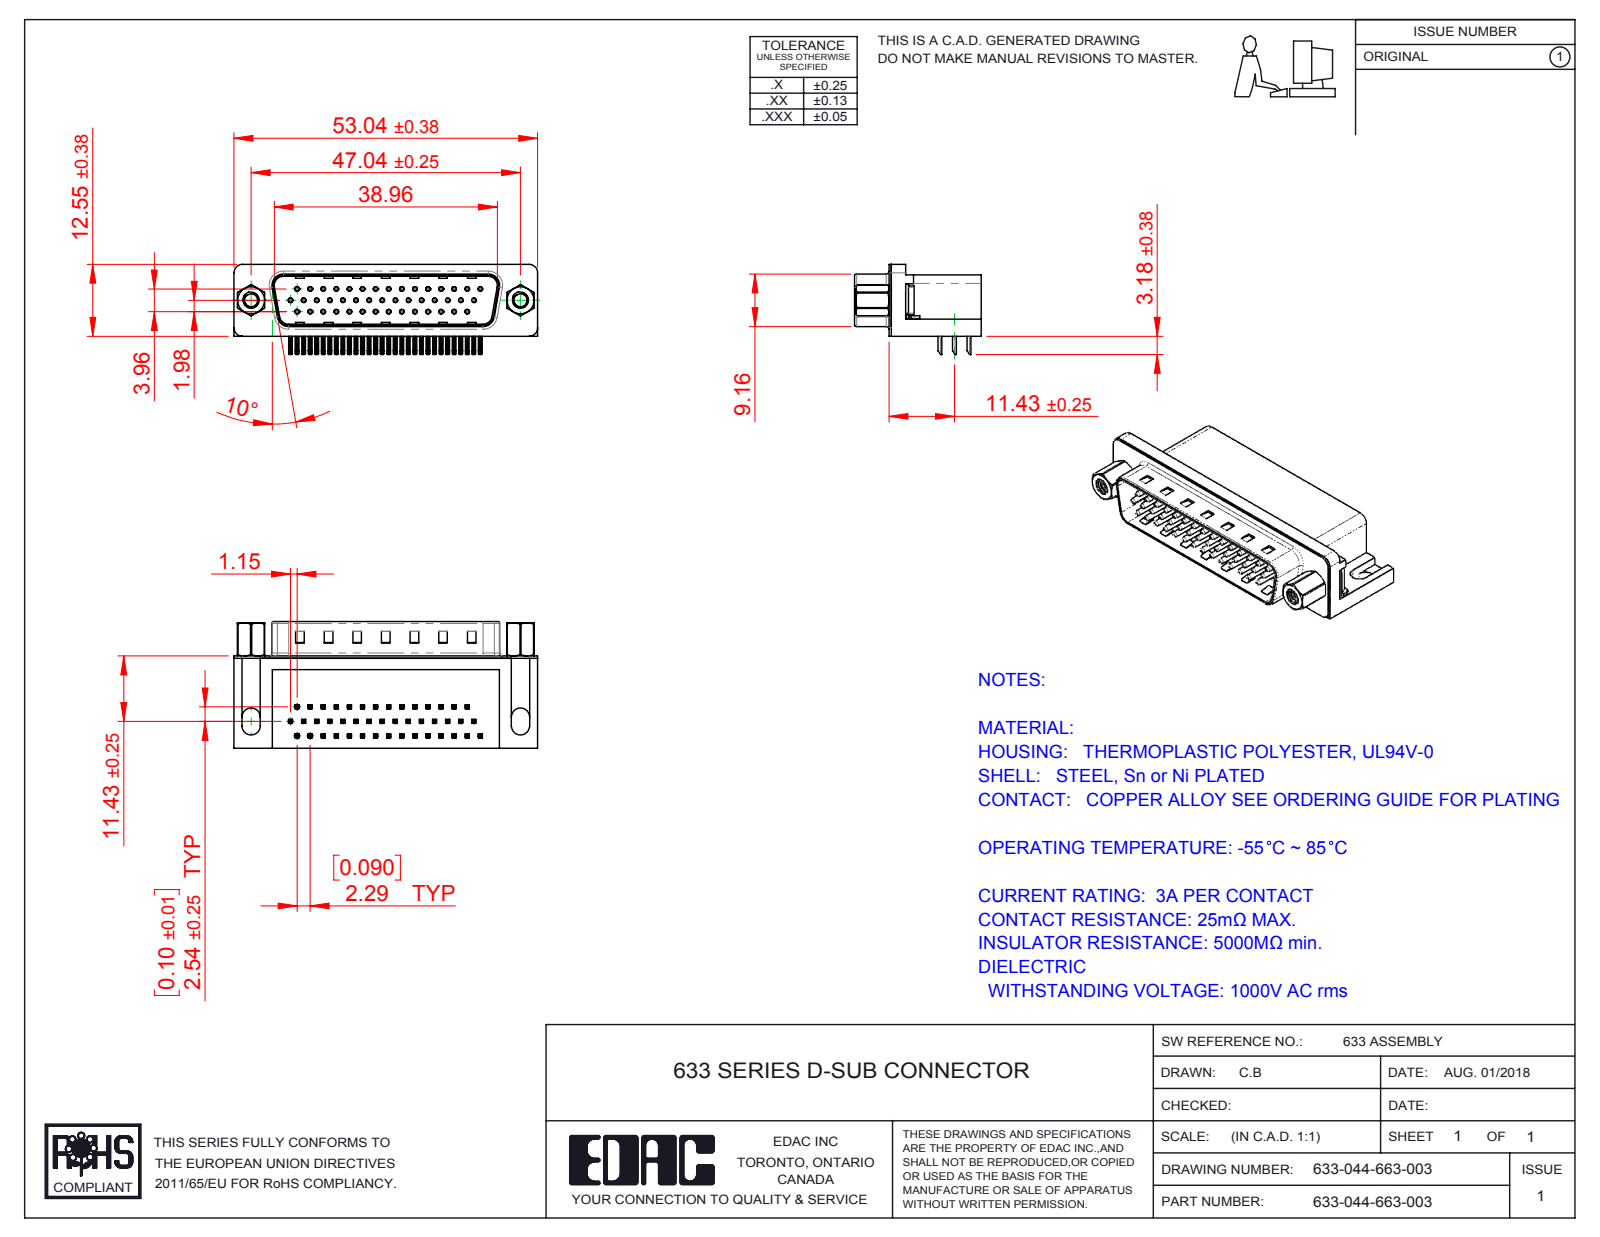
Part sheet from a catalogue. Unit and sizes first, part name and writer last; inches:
Units: inches
Overall size (bounding box): 2.088 × 0.87 × 0.619
Round holes (diameter × count): ⌀0.014 ×44, ⌀0.031 ×44, ⌀0.089 ×2, ⌀0.09 ×2, ⌀0.157 ×2, ⌀0.189 ×2, ⌀0.197 ×2
Round bosses / shafts (diameter × count): ⌀0.03 ×44, ⌀0.193 ×2, ⌀0.187 ×2, ⌀0.154 ×2, ⌀0.11 ×2
Partial cylindrical surfaces — rounded edges, fillets, slot ends (radius × count): R0.01 ×184, R0.005 ×88, R0.039 ×16, R0.02 ×9, R0.063 ×8, R0.059 ×7, R0.035 ×4, R0.079 ×4
Main face-to-face distances: 0.016, 0.407, 0.618, 0.345, 0.114, 0.098, 0.634, 0.083, 0.421, 0.1
Hole centre spacings: 0.09, 0.18, 0.18, 0.09, 0.27, 0.361, 0.451, 0.089
Volume: 0.505 in³ · Surface area: 16.19 in²
Bodies: 52 solids, 3806 faces (2339 planar, 1120 cylindrical, 347 other)
Part name (STEP PRODUCT): 633 Contact Bottom; 633 4-40 Hex Standoff; 633 Contact Middle; 633-044-663-003 (+5 more)
STEP written by: SolidWorks 2016 (CONFIG_CONTROL_DESIGN)
